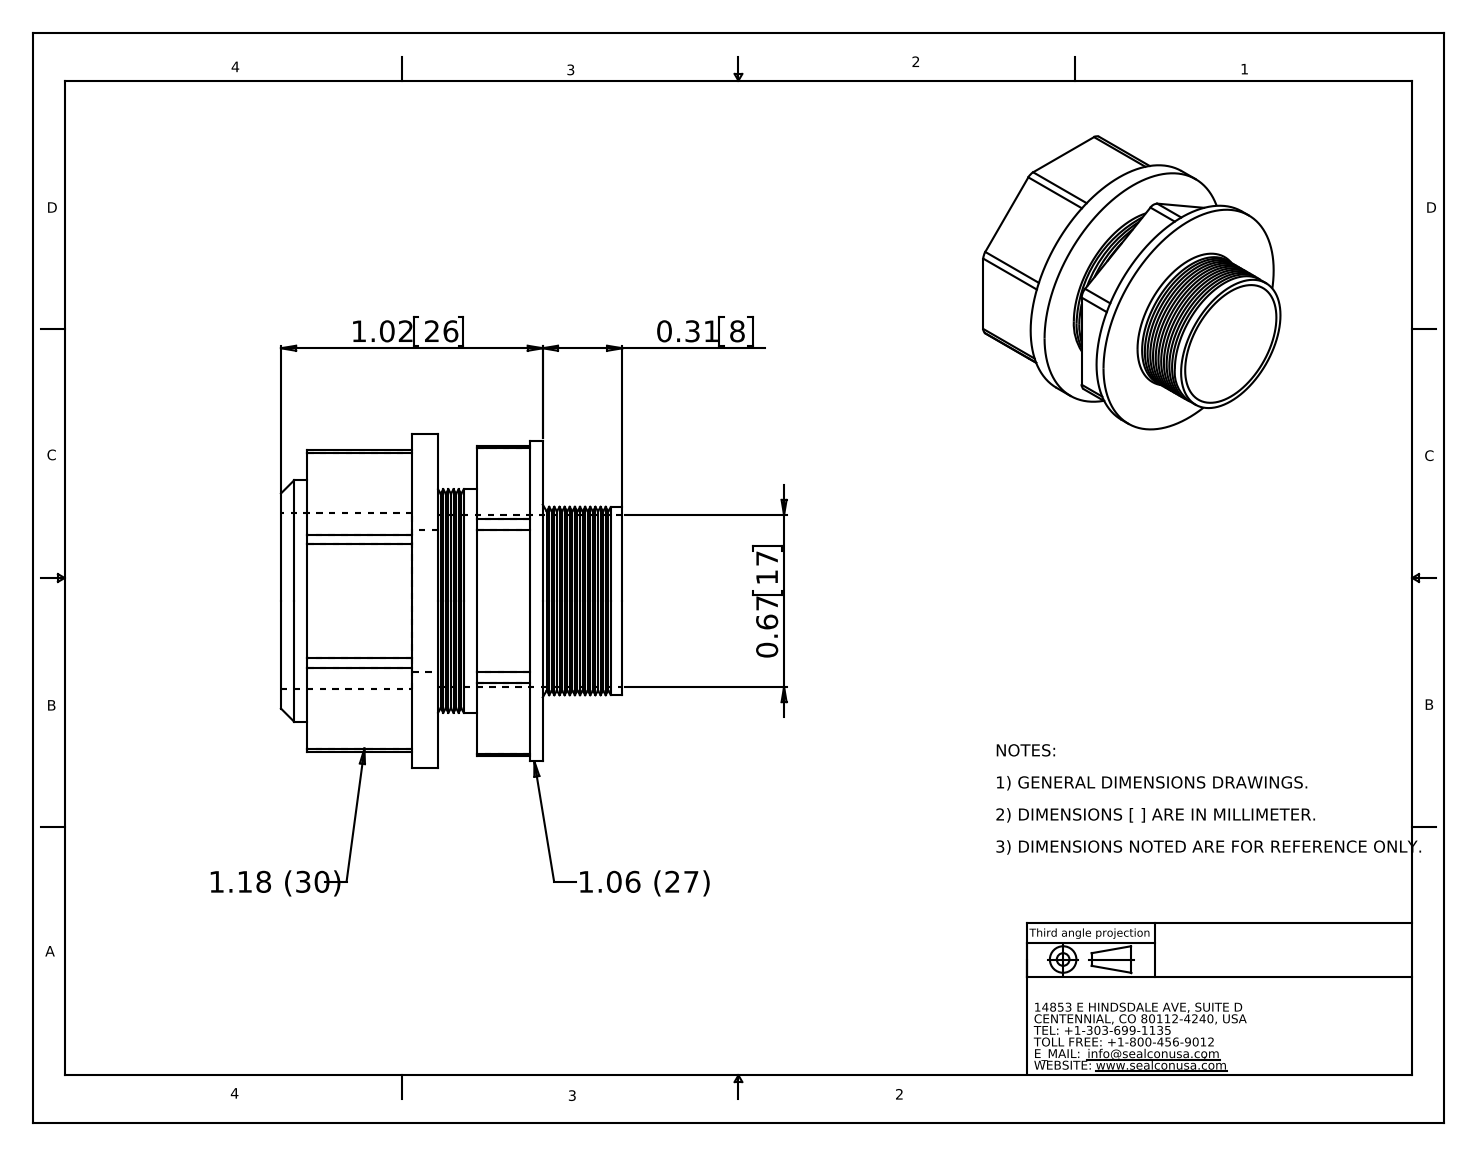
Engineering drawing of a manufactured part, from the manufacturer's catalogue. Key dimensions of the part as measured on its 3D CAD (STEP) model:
Part name (STEP PRODUCT): ST16AA-BK
STEP written by: SolidWorks 2008 (CONFIG_CONTROL_DESIGN)
Units: inches
Bodies: 2 solids, 128 faces (24 planar, 30 cylindrical, 74 other)
Overall size (bounding box): 1.33 × 1.3 × 1.3
Volume: 0.681 in³ · Surface area: 11.83 in²
Round holes (diameter × count): ⌀0.55 ×1, ⌀0.67 ×1, ⌀0.687 ×1
Round bosses / shafts (diameter × count): ⌀1.3 ×1, ⌀1.25 ×1, ⌀0.94 ×1, ⌀0.87 ×1, ⌀0.73 ×1
Partial cylindrical surfaces — rounded edges, fillets, slot ends (radius × count): R0.05 ×14
Main face-to-face distances: 0.408, 0.51, 0.255, 0.918, 0.663, 0.153, 1.18, 1.18, 0.102, 1.06
